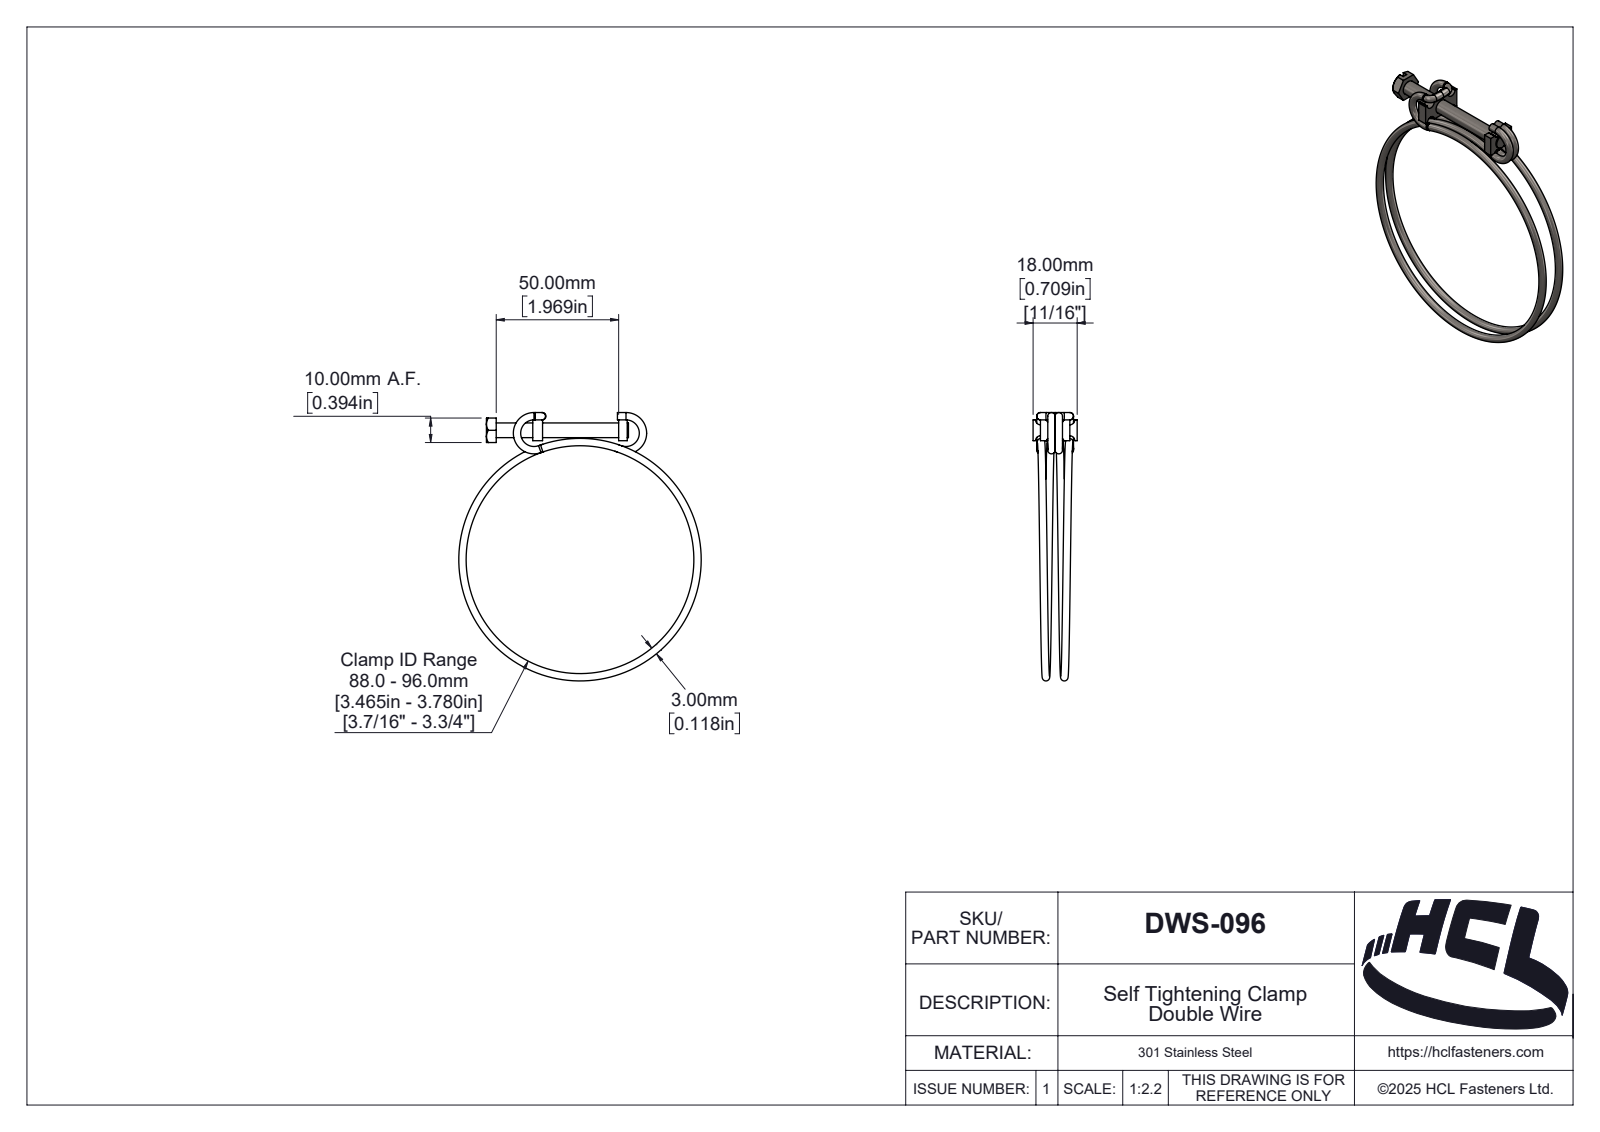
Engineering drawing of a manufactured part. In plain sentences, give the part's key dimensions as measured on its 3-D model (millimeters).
The part is named "DWS-096". Its 3-D file was written by "SolidWorks 2025 (AUTOMOTIVE_DESIGN)". It is 6 solids with 213 faces: 55 planar, 74 cylindrical and 84 other. Overall it measures 109.55 by 99 by 18 millimeters. Its volume is 8 024 cubic millimeters and its surface area 9 701 square millimeters. Round holes: 1 of diameter 6. Round bosses or shafts: 4 of diameter 3. Partial cylindrical surfaces (rounded edges, fillets, slot ends): 12 of radius 0.2, 4 of radius 1, 4 of radius 2, 1 of radius 0.4, 1 of radius 0.51, 1 of radius 0.53, 1 of radius 0.64, 1 of radius 0.91. The main face-to-face distances are 4, 18.92, 10, 35.08, 3, 54, 34.58, 53.5, 1, 38.58.
